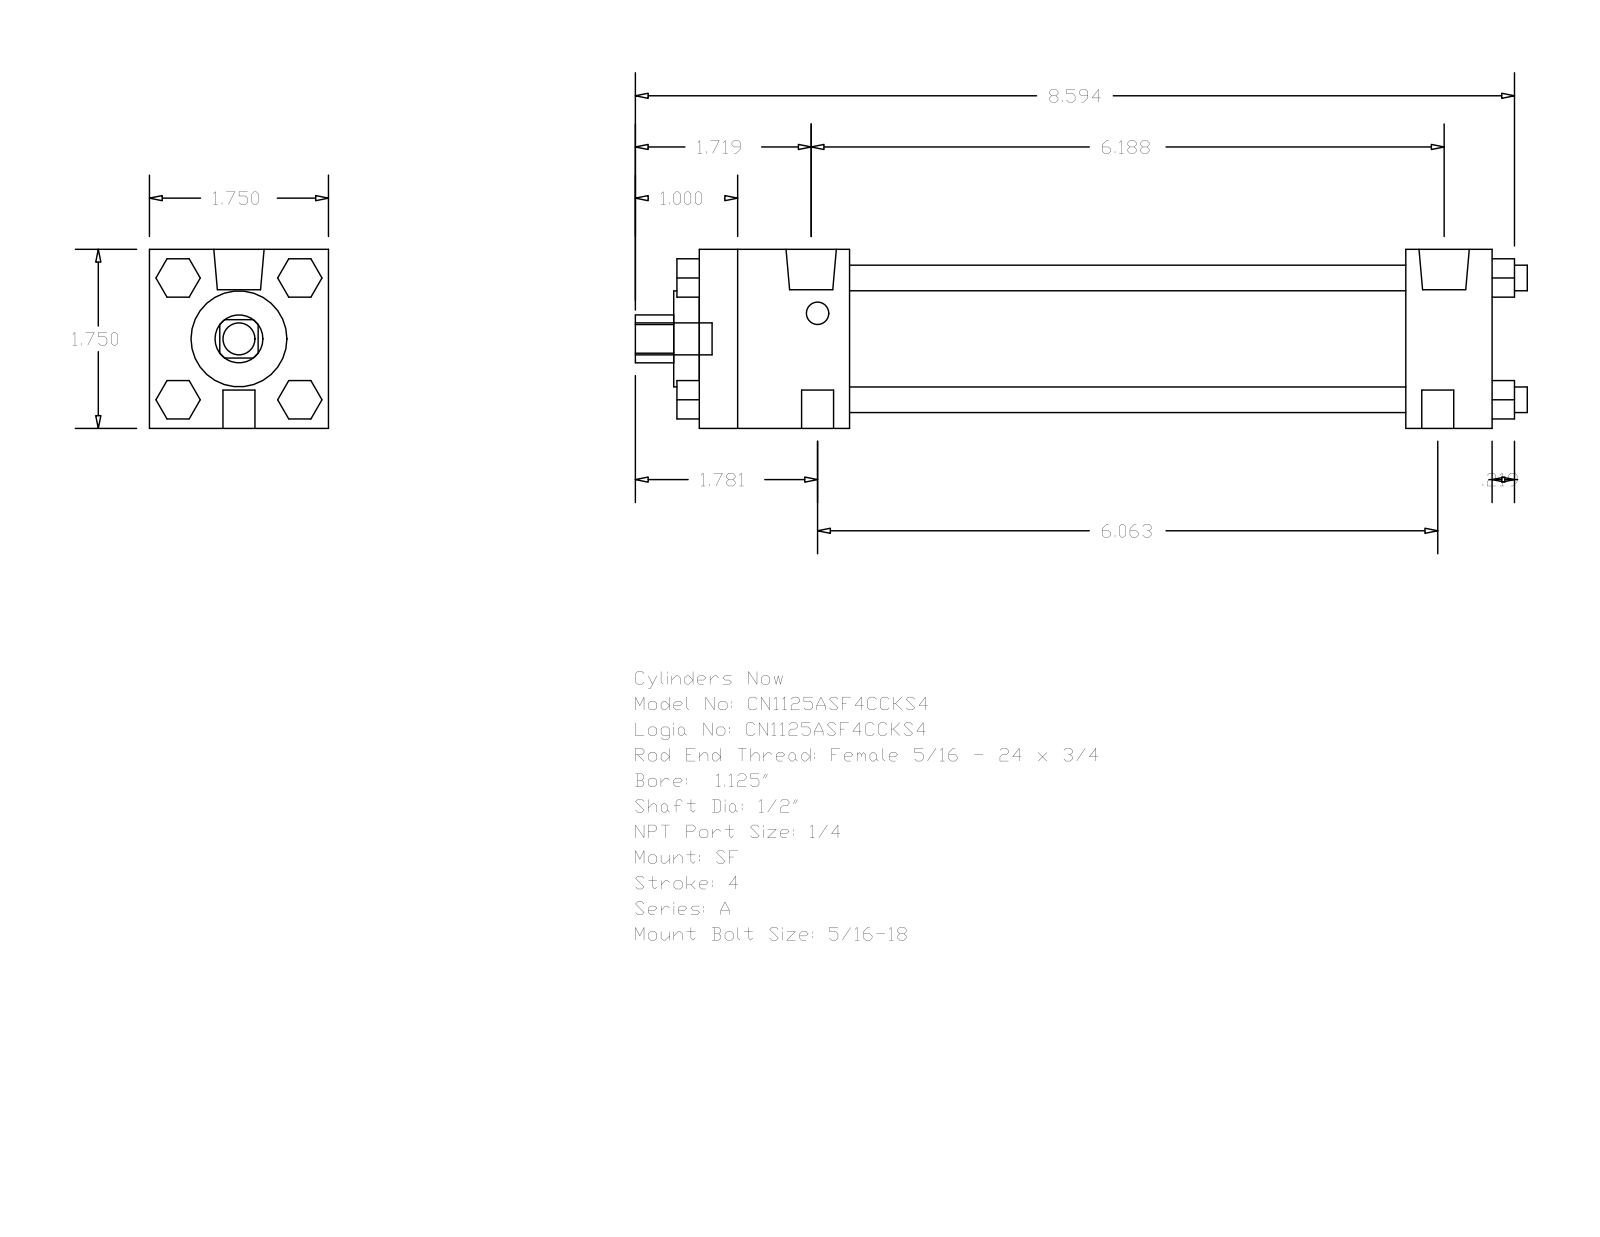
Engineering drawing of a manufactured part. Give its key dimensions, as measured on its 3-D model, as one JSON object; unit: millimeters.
{"part_name": "A_SF__0112_0.5", "step_written_by": "GSSL Pune (CONFIG_CONTROL_DESIGN)", "units": "millimeters", "bodies": {"solids": 0, "faces": 120, "planar": 92, "cylindrical": 28, "other": 0}, "overall_size": [221.46, 44.45, 44.45], "round_holes": [[12.7, 1], [23.81, 1], [31.88, 1]], "round_bosses_or_shafts": [[6.35, 4], [7.94, 3], [12.49, 2], [5.56, 2]], "partial_cylinders_radius": [[5.94, 1]], "face_to_face_distances": [44.46, 196.84, 175.41, 21.43, 37.3, 138.11, 159.54, 9.53, 5.59, 9.52]}
